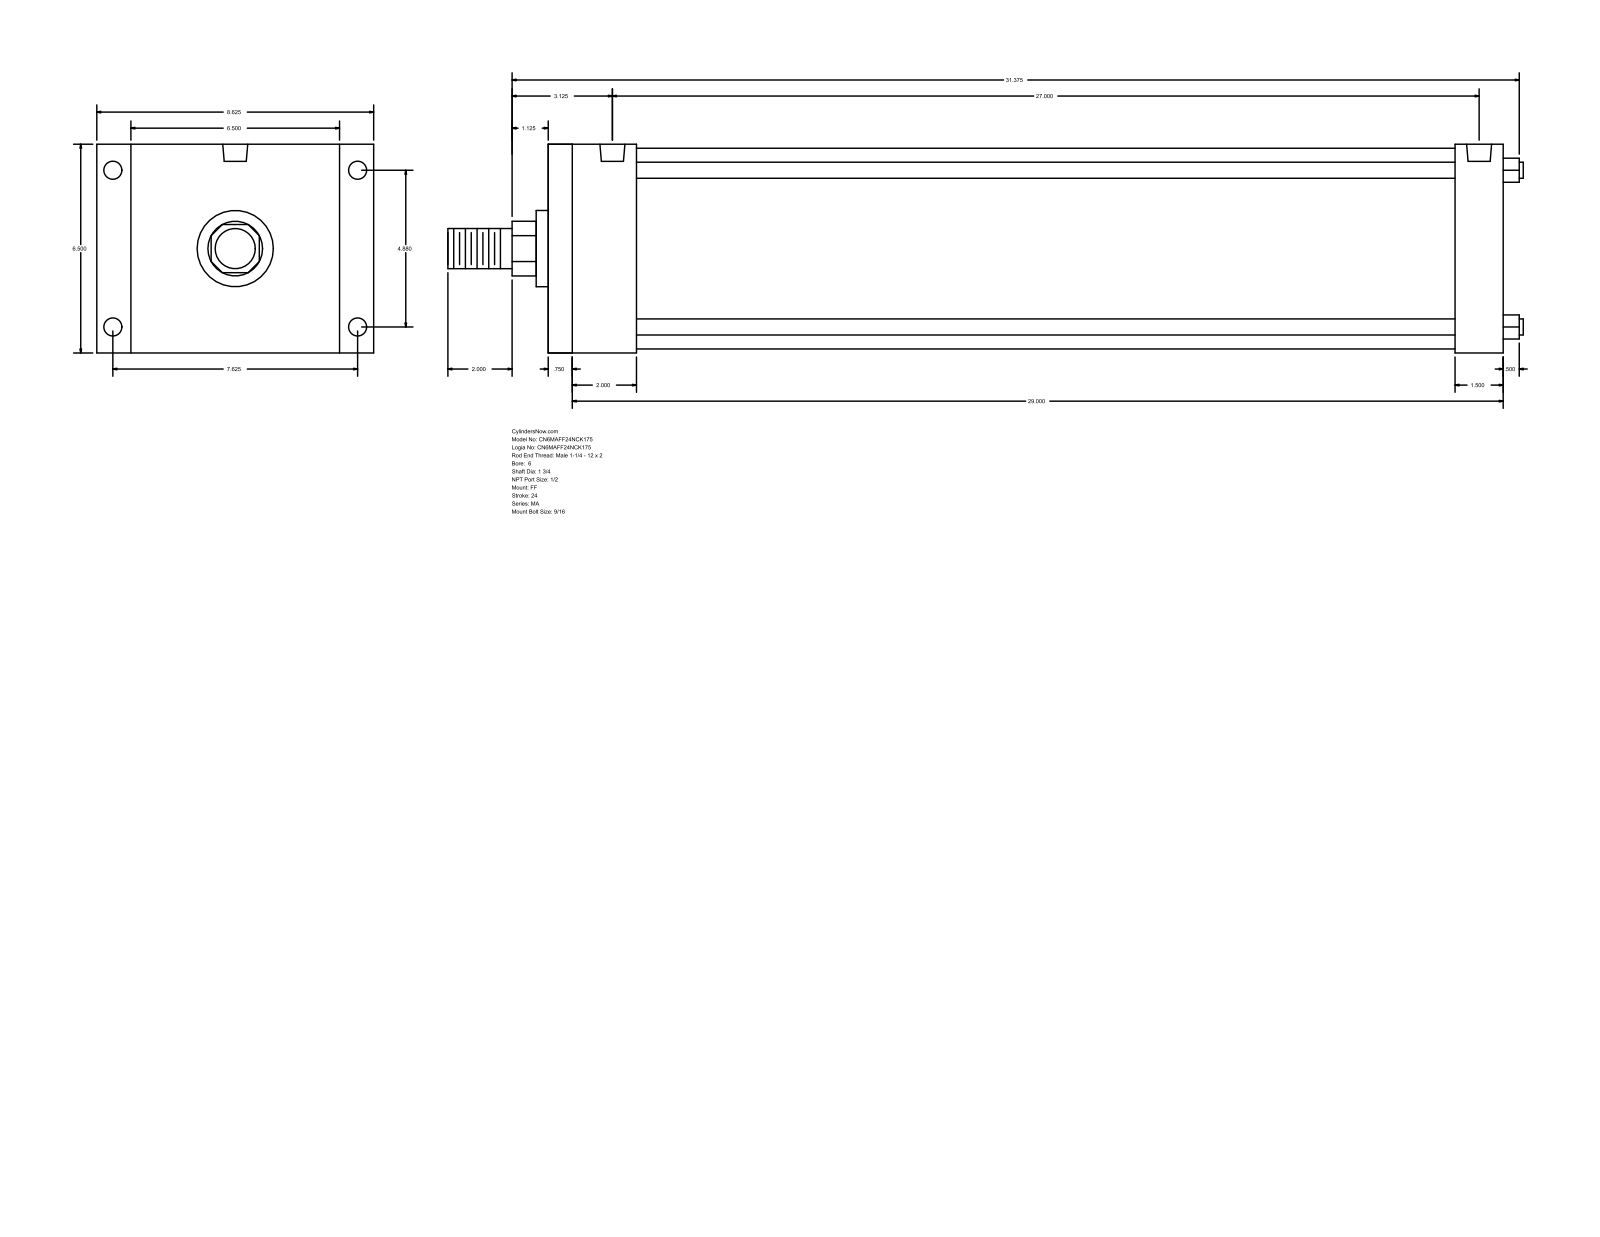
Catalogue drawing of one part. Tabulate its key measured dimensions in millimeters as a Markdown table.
| quantity | value |
| --- | --- |
| part name | MA_FF__0600_1.75 |
| STEP written by | GSSL Pune (CONFIG_CONTROL_DESIGN) |
| units | millimeters |
| bodies | 0 solids, 92 faces (64 planar, 28 cylindrical, 0 other) |
| overall size | 850.9 × 219.07 × 165.1 |
| round holes (diameter × count) | 14.29 × 4, 17.46 × 4, 19.77 × 2 |
| round bosses / shafts (diameter × count) | 12.7 × 4, 158.75 × 1, 60.33 × 1, 44.45 × 1, 31.75 × 1 |
| partial cylindrical surfaces (radius × count) | 21.63 × 1 |
| main face-to-face distances | 165.1, 755.66, 19.05, 736.61, 50.8, 69.85, 698.5, 685.81, 717.55, 647.7 |
| hole center spacings | 123.96, 193.68, 229.95, 685.79 |
